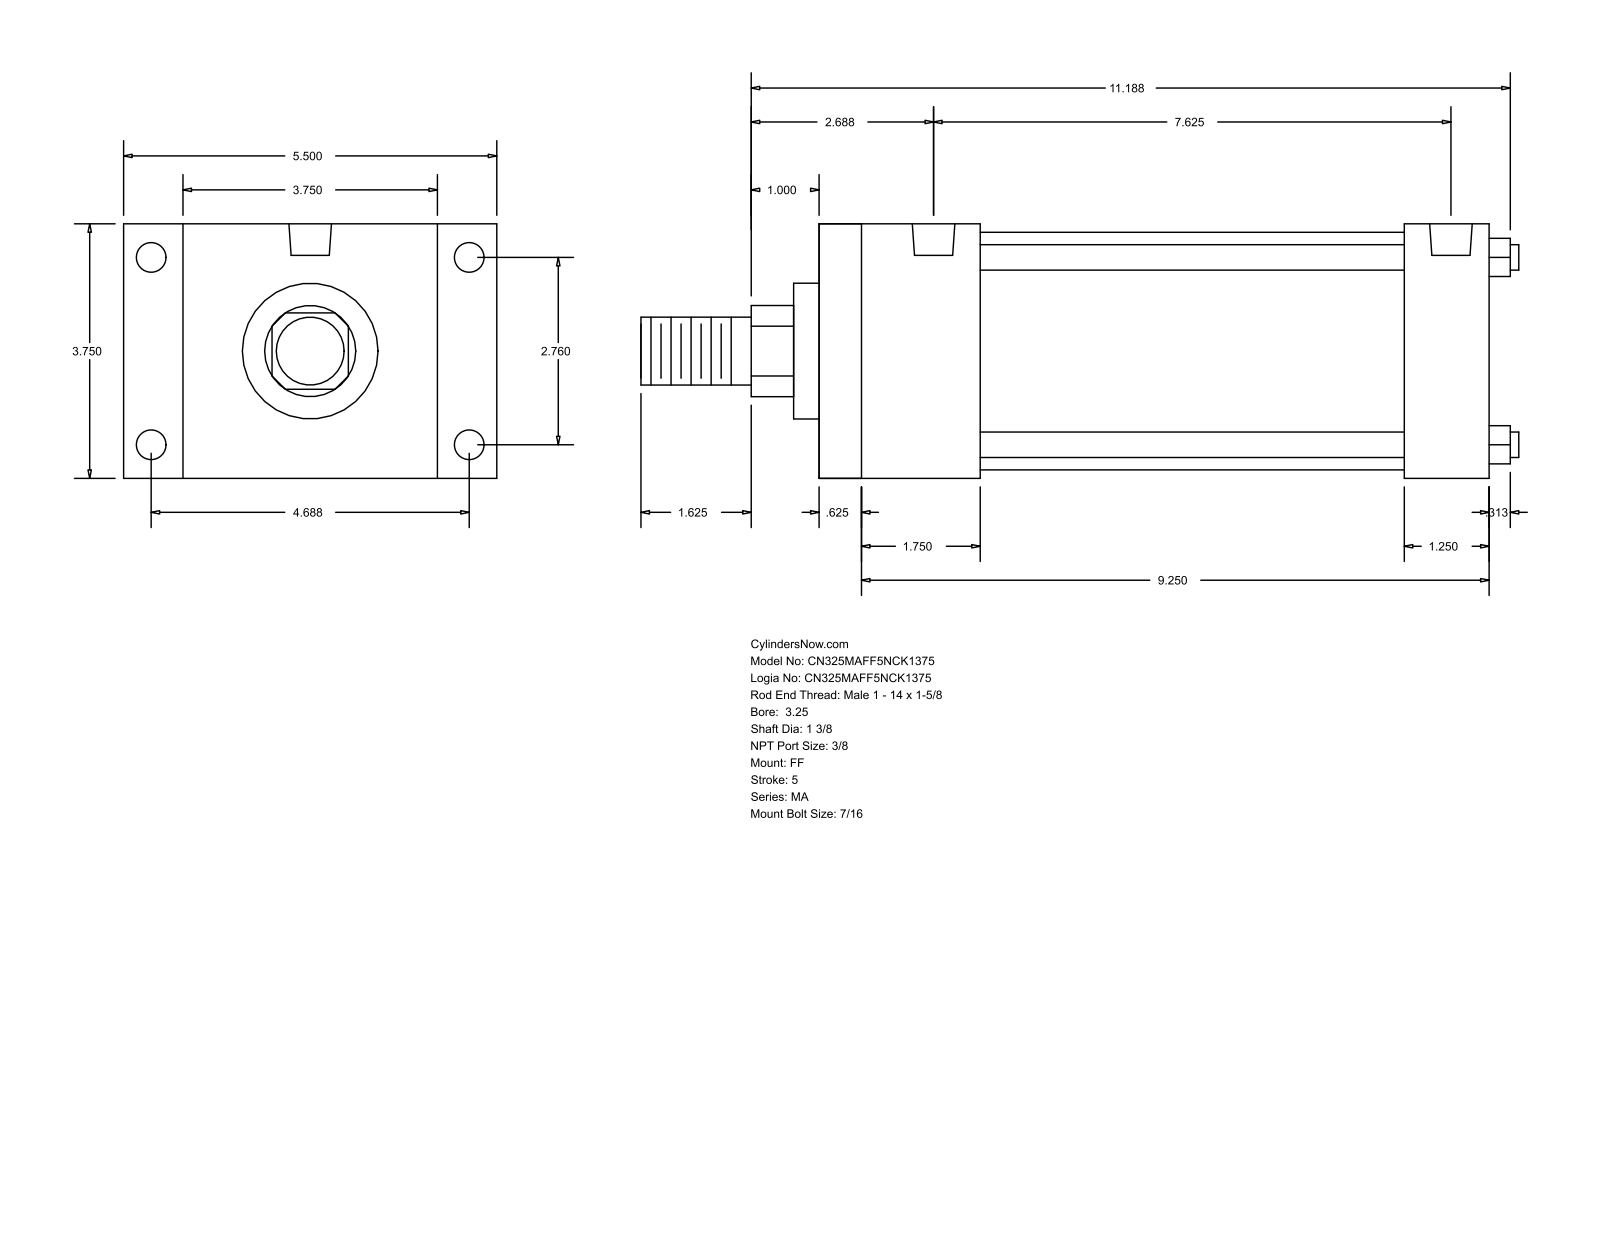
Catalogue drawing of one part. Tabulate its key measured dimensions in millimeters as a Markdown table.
| quantity | value |
| --- | --- |
| part name | MA_FF__0325_1.375 |
| STEP written by | GSSL Pune (CONFIG_CONTROL_DESIGN) |
| units | millimeters |
| bodies | 0 solids, 92 faces (64 planar, 28 cylindrical, 0 other) |
| overall size | 328.61 × 139.7 × 95.25 |
| round holes (diameter × count) | 11.11 × 8, 15.93 × 2 |
| round bosses / shafts (diameter × count) | 9.53 × 4, 88.9 × 1, 50.8 × 1, 34.92 × 1, 25.4 × 1 |
| partial cylindrical surfaces (radius × count) | 17.06 × 1 |
| main face-to-face distances | 95.24, 250.83, 15.87, 234.96, 22.23, 117.47, 60.32, 219.07, 44.45, 203.2 |
| hole center spacings | 70.1, 119.06, 138.16, 184.15, 4.76, 4.77, 188.91, 188.92 |
